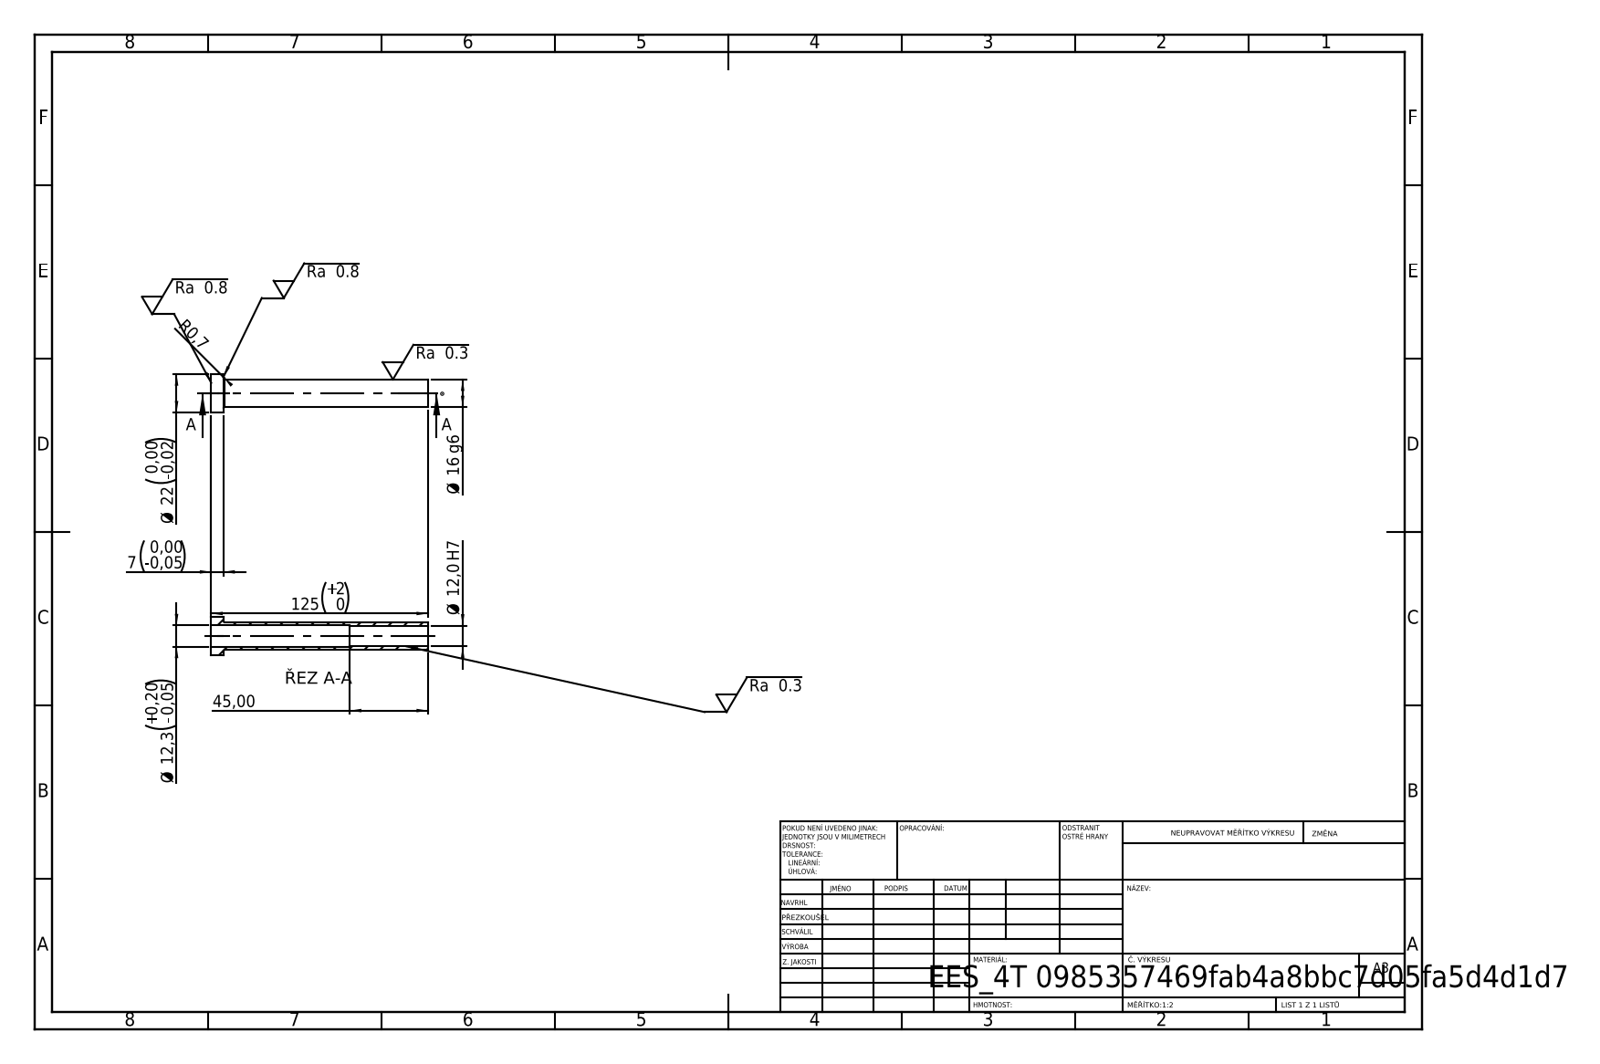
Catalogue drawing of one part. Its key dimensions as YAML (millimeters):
step_written_by: "SolidWorks 2019 (CONFIG_CONTROL_DESIGN)"
units: millimeters
bodies: {solids: 1, faces: 14, planar: 4, cylindrical: 8, other: 2}
overall_size: [125, 22, 22]
volume: 11796
surface_area: 11722
round_holes:
  - {diameter: 12, count: 1}
  - {diameter: 12.3, count: 1}
round_bosses_or_shafts:
  - {diameter: 22, count: 1}
  - {diameter: 16, count: 1}
face_to_face_distances: [7, 125, 118, 80, 73, 45]
